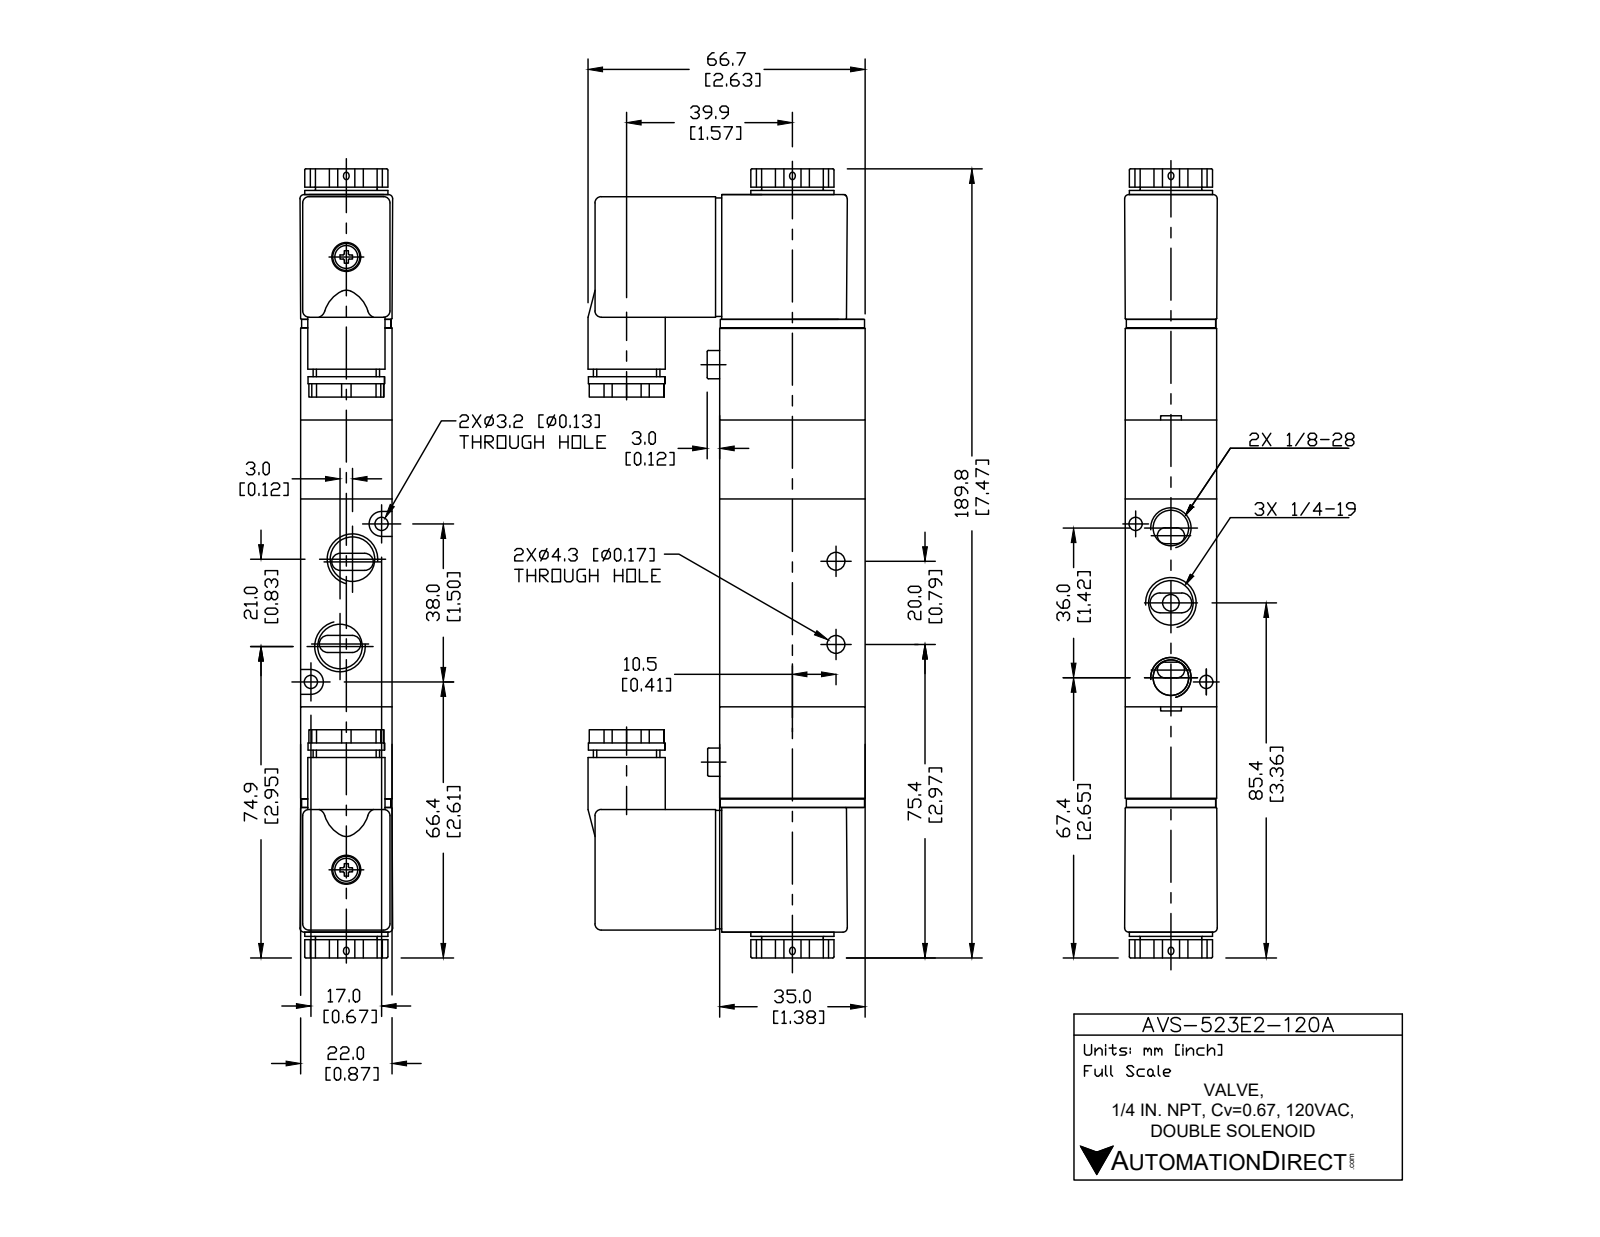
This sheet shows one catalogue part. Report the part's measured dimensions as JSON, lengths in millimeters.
{"part_name": "AVS-523E2-120A", "step_written_by": "SolidWorks 2015 (CONFIG_CONTROL_DESIGN)", "units": "millimeters", "bodies": {"solids": 5, "faces": 236, "planar": 129, "cylindrical": 91, "other": 16}, "overall_size": [189.82, 66.7, 22], "volume_mm3": 148738, "surface_area_mm2": 37934, "round_holes": [[11.13, 3], [3.2, 2], [4.3, 2], [8.43, 2], [9.3, 1]], "round_bosses_or_shafts": [[6.8, 2], [18.6, 1], [17.6, 1], [15.81, 1], [13.02, 1], [11, 1]], "partial_cylinders_radius": [[1.54, 10], [0.3, 8], [0.5, 8], [1, 8], [3, 2]], "face_to_face_distances": [0.88, 21.74, 1.95, 20.05, 22, 18.1, 22.62, 69, 30.59, 5.03], "hole_center_spacings": [8.56, 18, 20.81, 37.96, 7.54, 7.83, 10.53, 10.55]}
